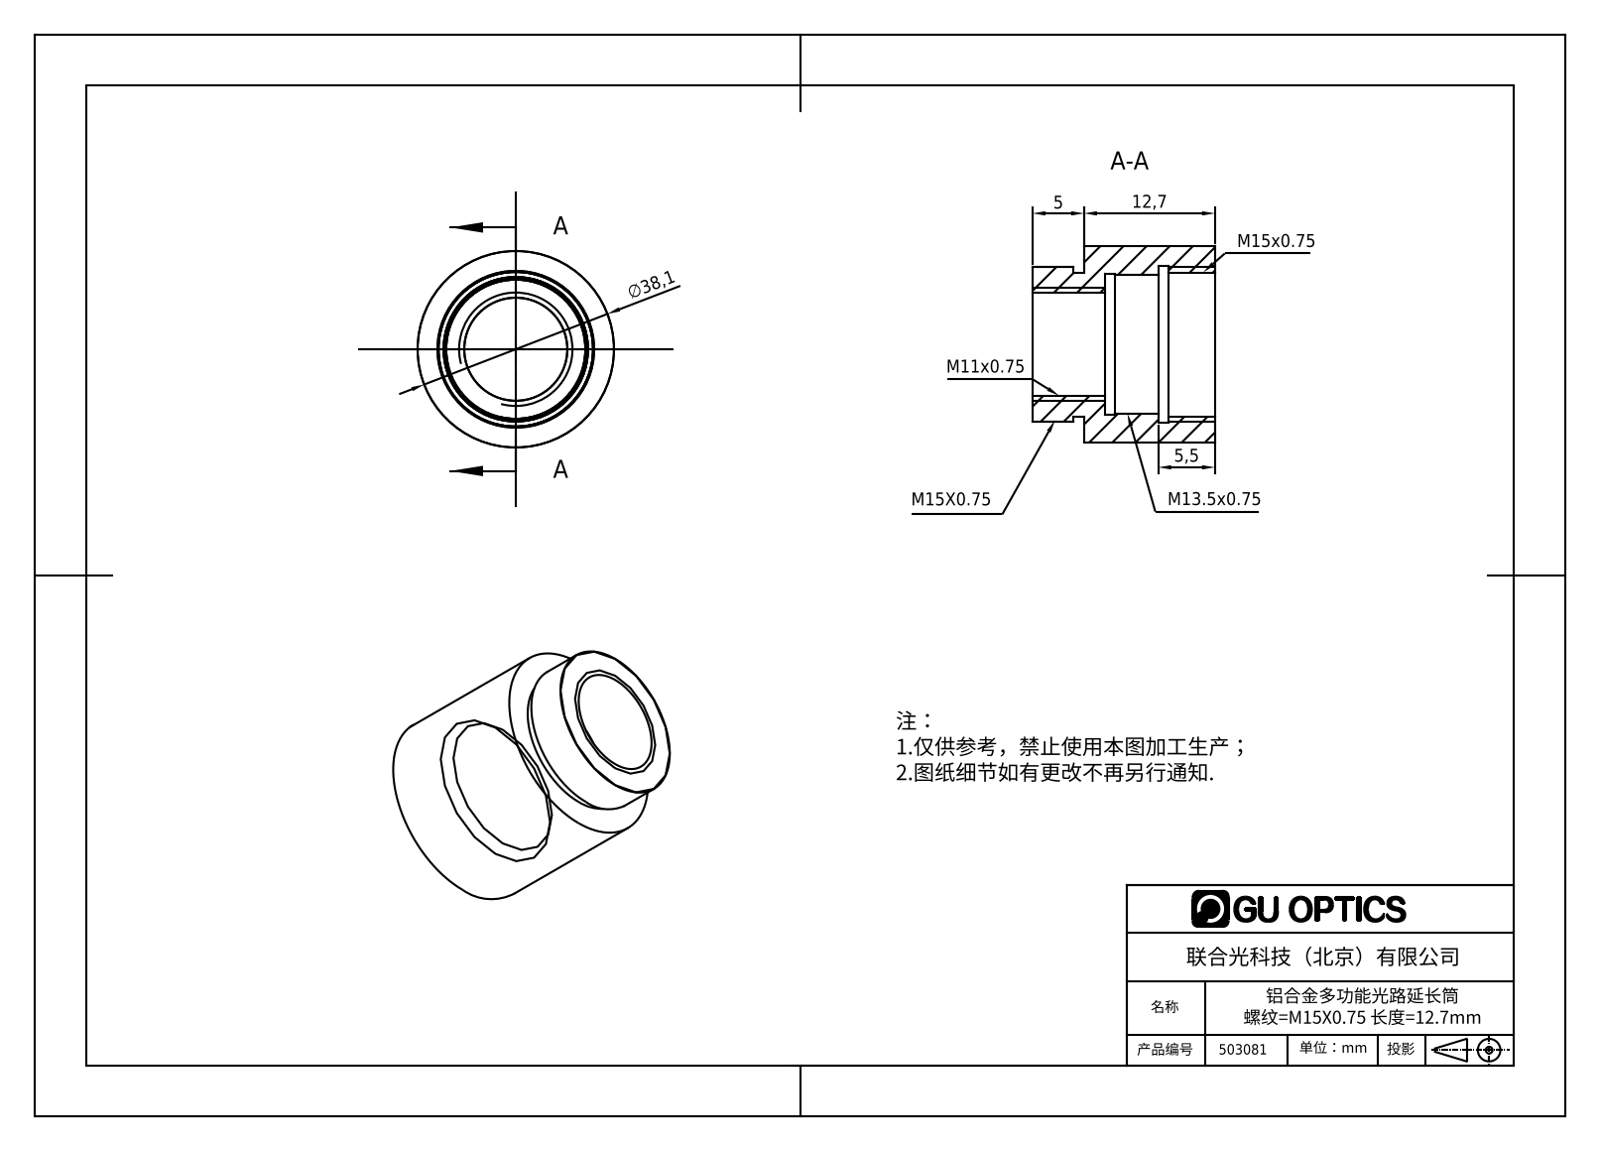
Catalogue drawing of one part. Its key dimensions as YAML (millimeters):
part_name: "503081"
step_written_by: "SolidWorks 2020 (CONFIG_CONTROL_DESIGN)"
units: millimeters
bodies: {solids: 1, faces: 24, planar: 8, cylindrical: 16, other: 0}
overall_size: [19.05, 19.05, 17.7]
volume: 2308
surface_area: 2201
round_holes:
  - {diameter: 10, count: 1}
  - {diameter: 13.5, count: 1}
  - {diameter: 13.7, count: 1}
  - {diameter: 14, count: 1}
  - {diameter: 15.2, count: 1}
round_bosses_or_shafts:
  - {diameter: 19.05, count: 1}
  - {diameter: 15, count: 1}
face_to_face_distances: [12.7, 17.7, 5, 10.7, 2, 7, 1, 8.2, 5.2, 5.5]
